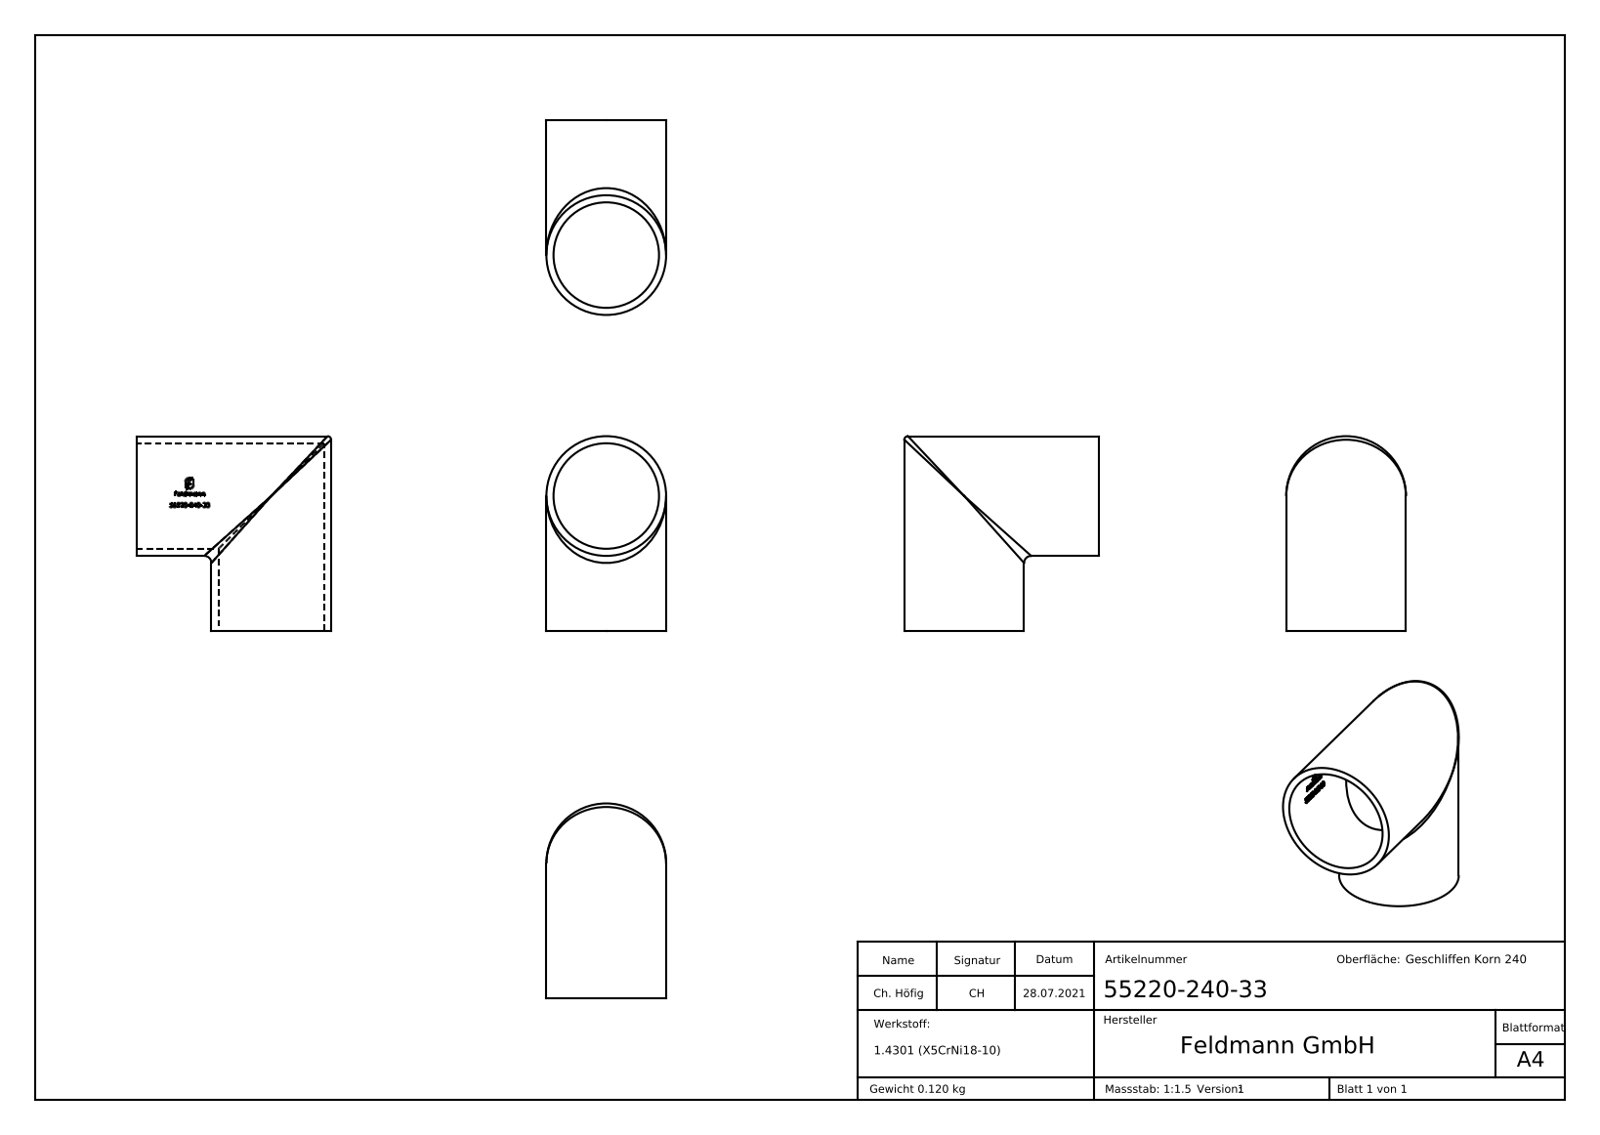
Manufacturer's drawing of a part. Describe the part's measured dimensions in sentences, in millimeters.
The part is named "55220-240-33". Its 3-D file was written by "SolidWorks 2018 (CONFIG_CONTROL_DESIGN)". It is 1 solid with 316 faces: 135 planar, 31 cylindrical and 150 other. Overall it measures 54.85 by 54.85 by 33.7 millimeters. Its volume is 15 150 cubic millimeters and its surface area 15 524 square millimeters. Round holes: 2 of diameter 29.7. Round bosses or shafts: 2 of diameter 33.7. Partial cylindrical surfaces (rounded edges, fillets, slot ends): 1 of radius 14.95. The main face-to-face distances are 1.82, 0.75, 0.88, 2.68, 34.8, 0.34, 0.61, 3.96, 0.44, 13.99.
